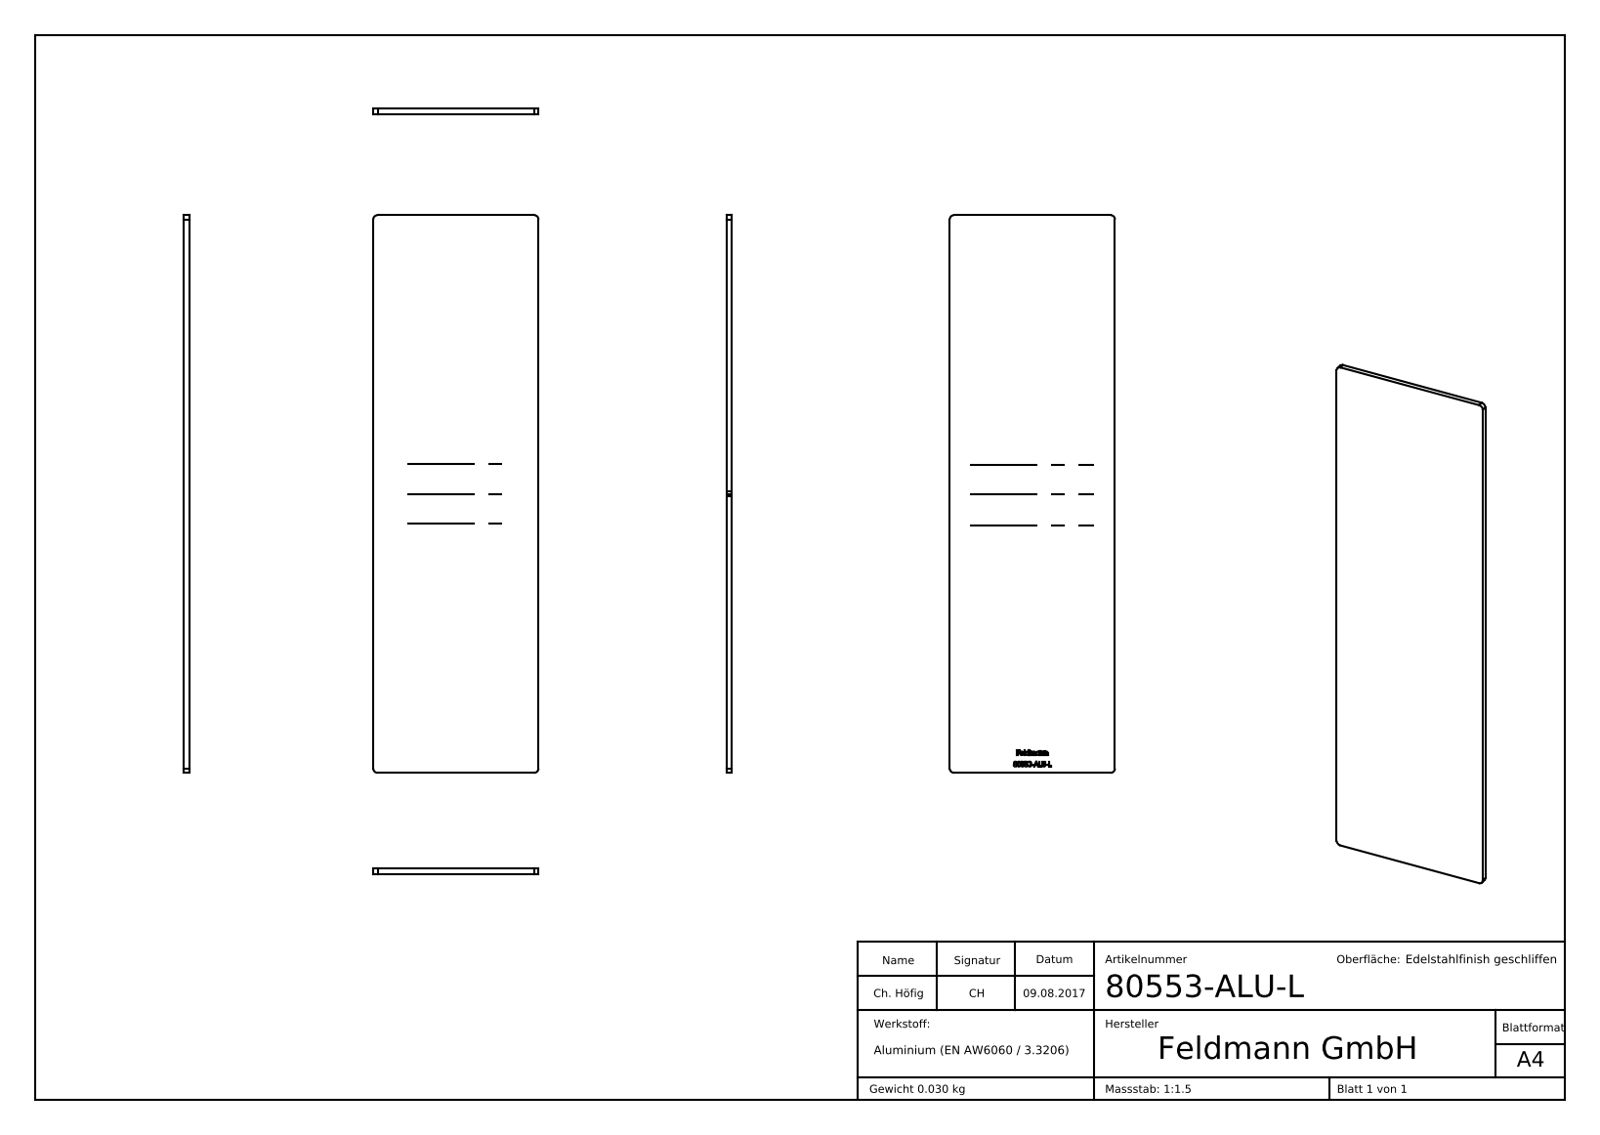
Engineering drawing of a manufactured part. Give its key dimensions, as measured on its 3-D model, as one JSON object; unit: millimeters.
{"part_name": "80553-ALU-L", "step_written_by": "SolidWorks 2015 (CONFIG_CONTROL_DESIGN)", "units": "millimeters", "bodies": {"solids": 1, "faces": 253, "planar": 138, "cylindrical": 4, "other": 111}, "overall_size": [157, 46.5, 1.5], "volume_mm3": 10948, "surface_area_mm2": 15216, "partial_cylinders_radius": [[1.2, 4]], "face_to_face_distances": [1.5, 46.5, 157, 1.4, 1.19, 5.62, 2.98, 4.23, 2.64, 8.89]}
